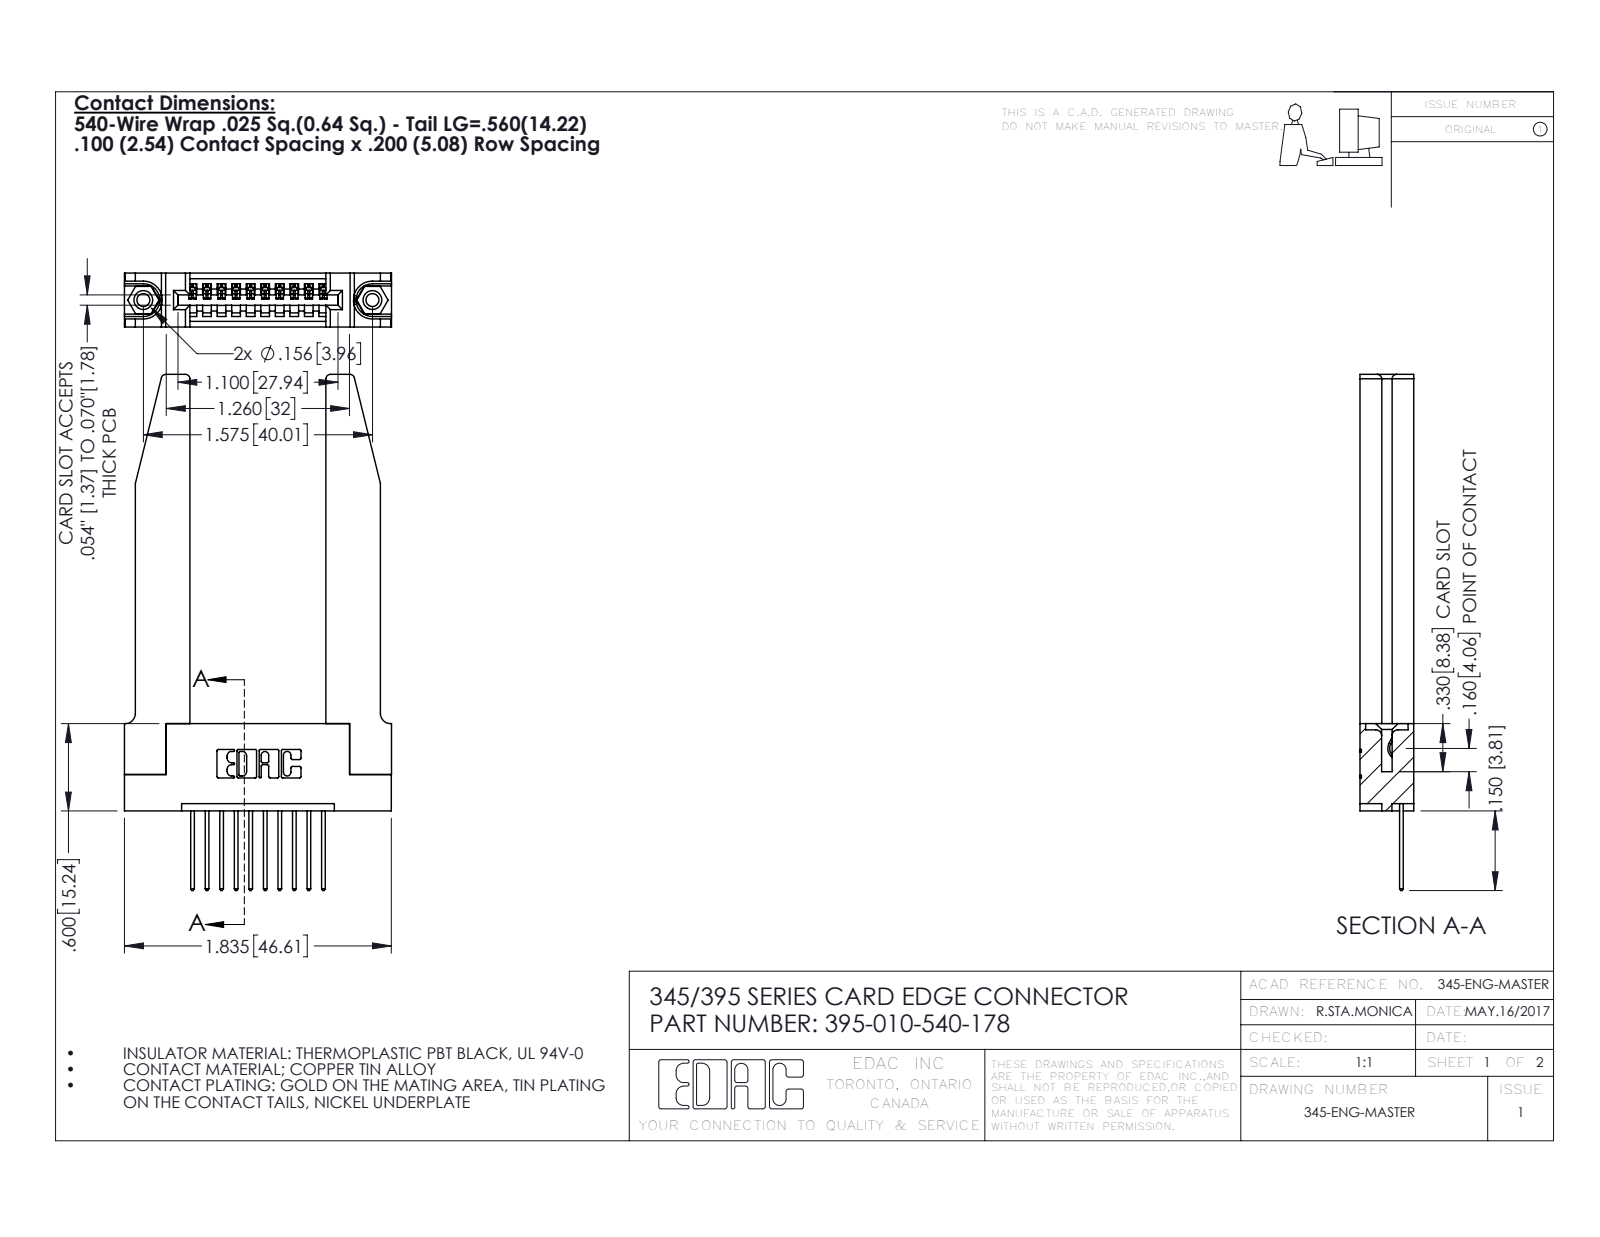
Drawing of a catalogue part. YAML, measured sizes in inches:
part_name: "345 Part_Flush Mounting Lugs - 0.156 Dia-TH; 345-220-078_345-220-078; 395-010-540-178; 345-292-001_345-293-140 (+1 more)"
step_written_by: "SolidWorks 2016 (CONFIG_CONTROL_DESIGN)"
units: inches
bodies: {solids: 15, faces: 940, planar: 622, cylindrical: 266, other: 52}
overall_size: [3.547, 1.836, 0.37]
volume: 0.729
surface_area: 18.7
round_holes:
  - {diameter: 0.089, count: 2}
  - {diameter: 0.125, count: 2}
  - {diameter: 0.156, count: 2}
  - {diameter: 0.064, count: 1}
round_bosses_or_shafts:
  - {diameter: 0.155, count: 2}
partial_cylinders:
  - {radius: 0.01, count: 22}
  - {radius: 0.006, count: 20}
  - {radius: 0.01, count: 20}
  - {radius: 0.03, count: 8}
  - {radius: 0.007, count: 6}
  - {radius: 0.031, count: 6}
  - {radius: 0.026, count: 3}
  - {radius: 0.031, count: 2}
face_to_face_distances: [0.37, 0.072, 0.298, 0.15, 0.2, 0.148, 0.22, 0.077, 0.935, 0.098]
hole_center_spacings: [0.27, 1.344, 1.575]
